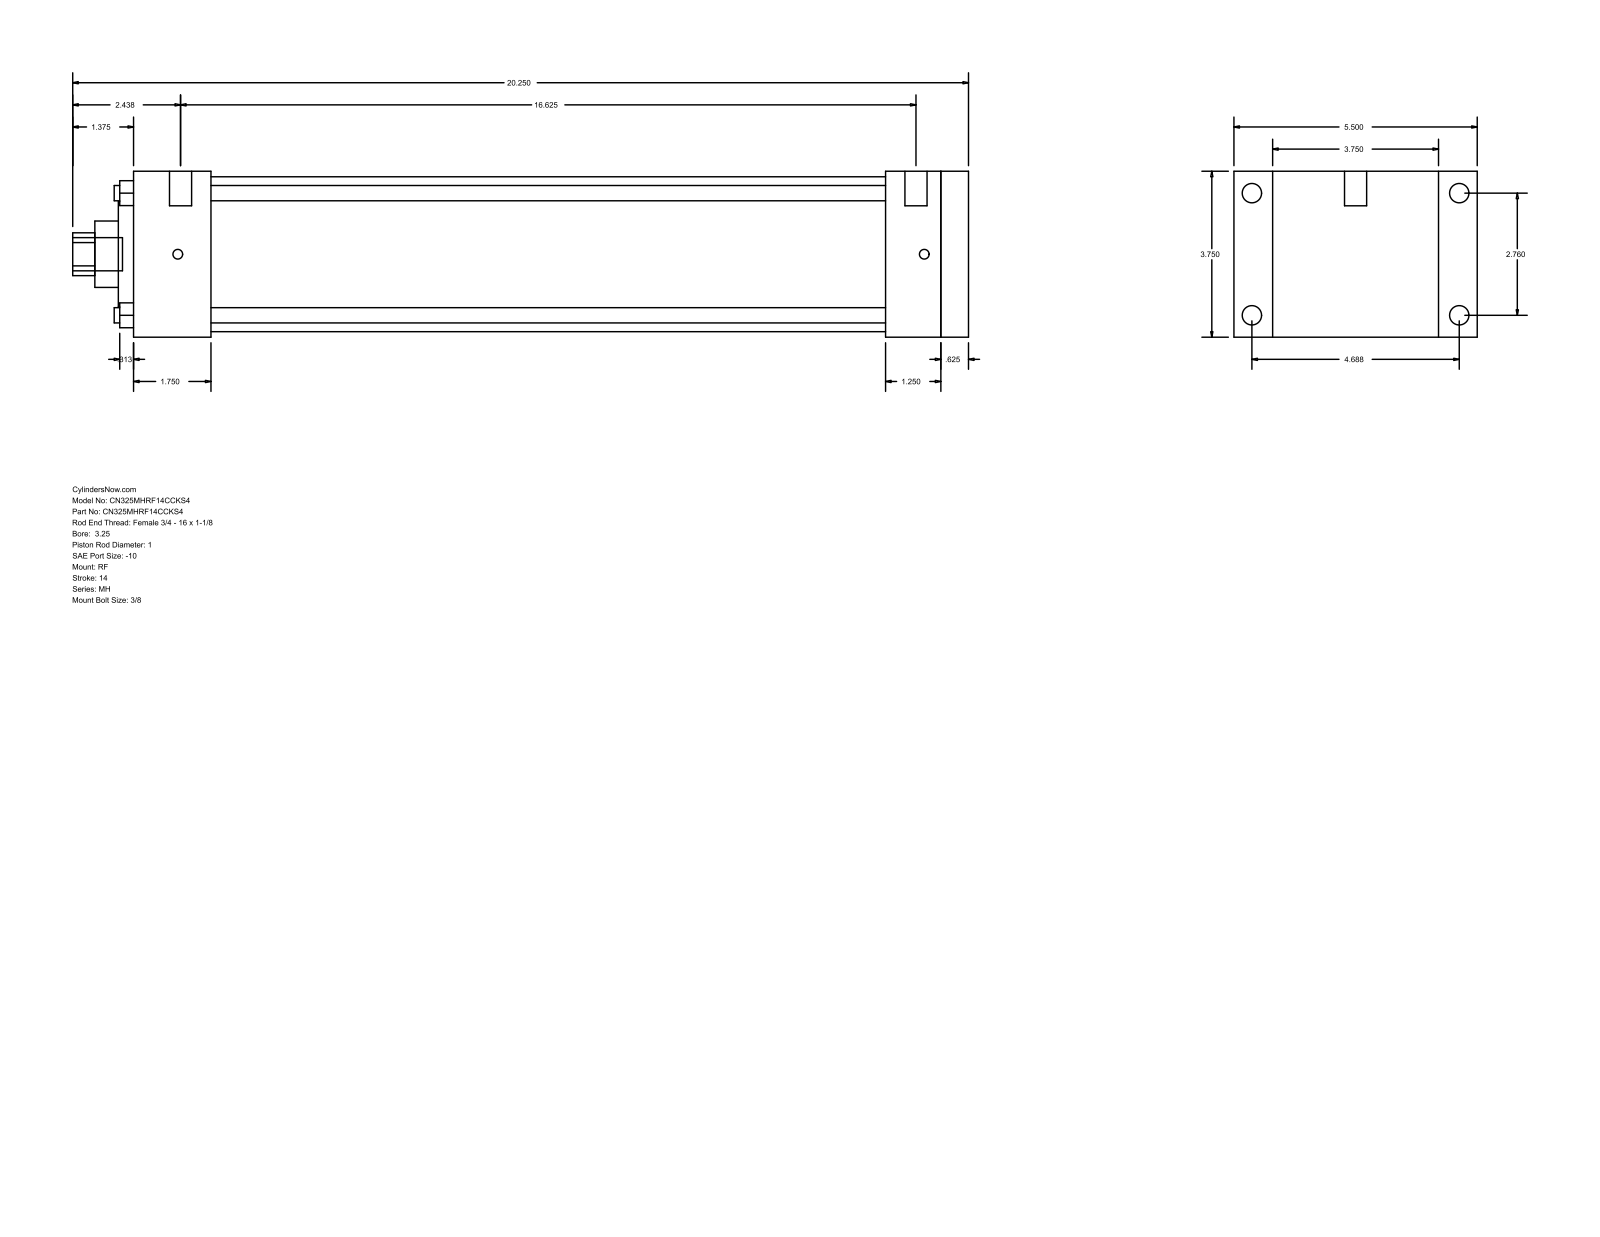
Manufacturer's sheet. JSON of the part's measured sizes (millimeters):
{"part_name": "MH_RF__0325_1", "step_written_by": "GSSL Pune (CONFIG_CONTROL_DESIGN)", "units": "millimeters", "bodies": {"solids": 0, "faces": 94, "planar": 65, "cylindrical": 29, "other": 0}, "overall_size": [514.35, 139.7, 95.25], "round_holes": [[8.76, 4], [25.4, 1], [38.1, 1], [60.33, 1], [88.9, 1]], "round_bosses_or_shafts": [[11.13, 4], [5.56, 4], [12.7, 2], [19.05, 1]], "partial_cylinders_radius": [[12.29, 1]], "face_to_face_distances": [95.24, 479.43, 15.87, 463.56, 22.23, 117.47, 44.46, 419.1, 434.97, 431.81], "hole_center_spacings": [49.57, 70.1, 99.14]}
